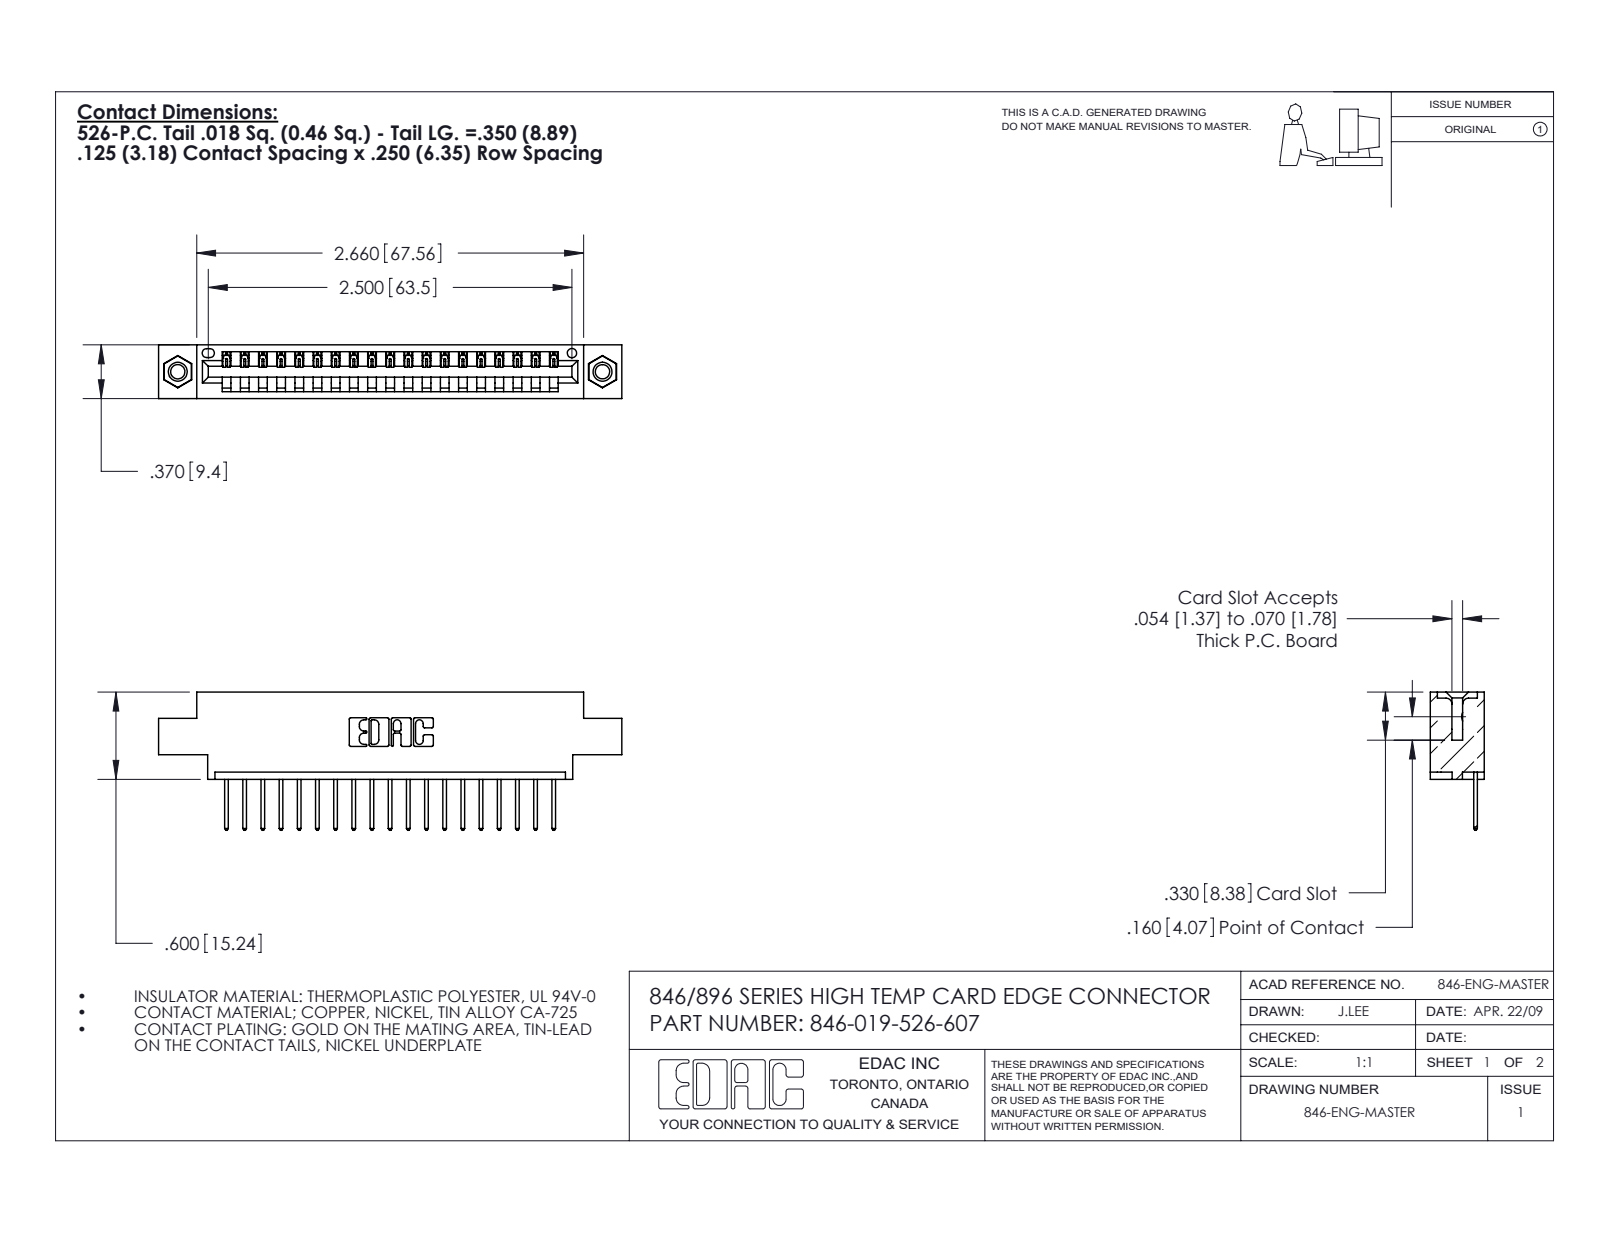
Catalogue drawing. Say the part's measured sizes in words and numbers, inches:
The part is named "345-292-001_345-293-126; 346-019-526-607; 346 Part_0.170 Offset - 0.156 Dia-TI; 345-250-001_345-250-005-103". Its 3-D file was written by "SolidWorks 2016 (CONFIG_CONTROL_DESIGN)". It is 22 solids with 1288 faces: 872 planar, 400 cylindrical and 16 other. Overall it measures 3.185 by 0.95 by 0.37 inches. Its volume is 0.452 cubic inches and its surface area 14.23 square inches. Round holes: 2 of diameter 0.098, 2 of diameter 0.125, 2 of diameter 0.156, 1 of diameter 0.064. Round bosses or shafts: 2 of diameter 0.155. Partial cylindrical surfaces (rounded edges, fillets, slot ends): 38 of radius 0.006, 38 of radius 0.01, 22 of radius 0.01, 6 of radius 0.007, 6 of radius 0.031, 3 of radius 0.026, 2 of radius 0.031, 2 of radius 0.04. The main face-to-face distances are 0.048, 0.322, 0.37, 0.25, 0.072, 0.298, 0.025, 0.222, 0.148, 0.1. The hole center spacings are 0.246, 2.713, 2.92.
